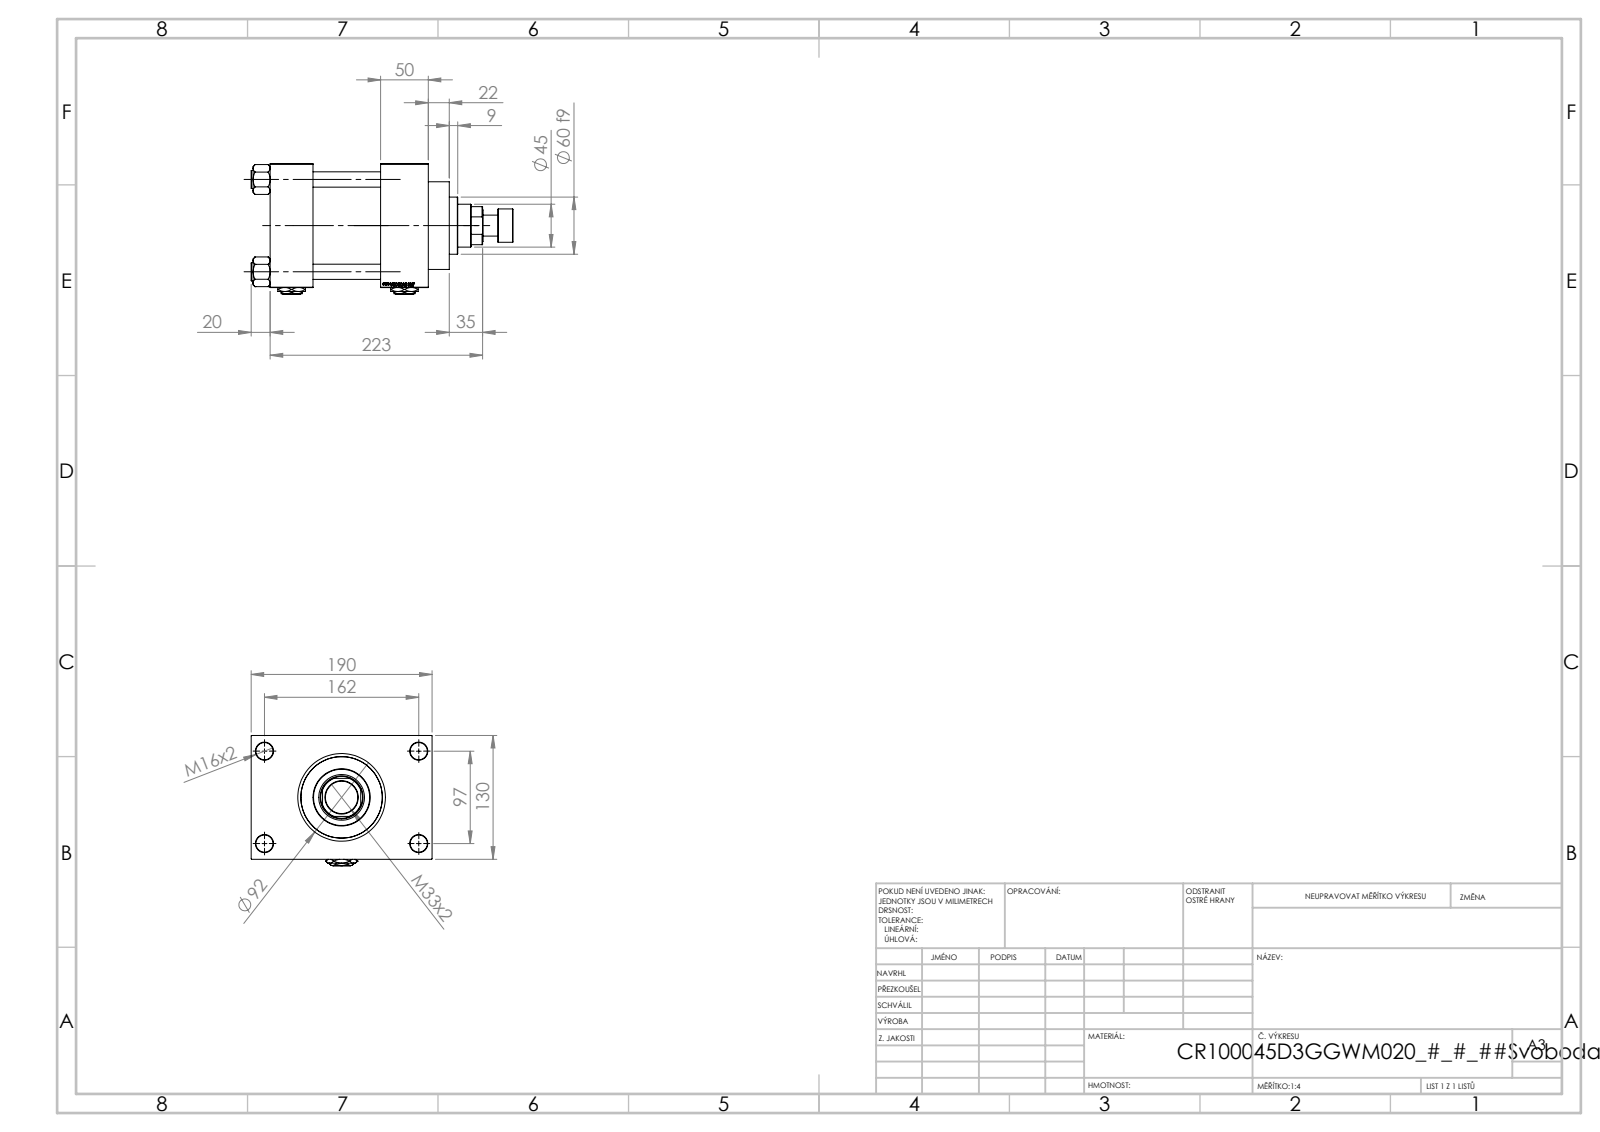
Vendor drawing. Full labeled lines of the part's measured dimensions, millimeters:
Part name (STEP PRODUCT): V215CR_VCP_D; NUT_M5_D; Zatka_pro_OIL_PORT; V215CR_D_TYCINKA (+3 more)
STEP written by: SolidWorks 2019 (CONFIG_CONTROL_DESIGN)
Units: millimetres
Bodies: 14 solids, 1267 faces (597 planar, 104 cylindrical, 566 other)
Overall size (bounding box): 275 × 190 × 137
Volume: 2 614 000 mm³ · Surface area: 365 097 mm²
Round holes (diameter × count): ⌀16 ×4, ⌀18 ×4, ⌀7 ×2, ⌀26.44 ×2, ⌀35 ×2, ⌀31.5 ×1, ⌀45 ×1, ⌀48 ×1, ⌀76 ×1, ⌀85.5 ×1, ⌀100 ×1
Round bosses / shafts (diameter × count): ⌀19 ×4, ⌀106 ×1, ⌀92 ×1, ⌀60 ×1, ⌀35 ×1, ⌀22 ×1
Partial cylindrical surfaces — rounded edges, fillets, slot ends (radius × count): R22 ×1
Main face-to-face distances: 130, 45, 116, 71, 166, 121, 50, 160, 30, 20
Hole centre spacings: 32.55, 68.52, 94.41, 96.9, 102.27, 129.45, 161.73, 97
